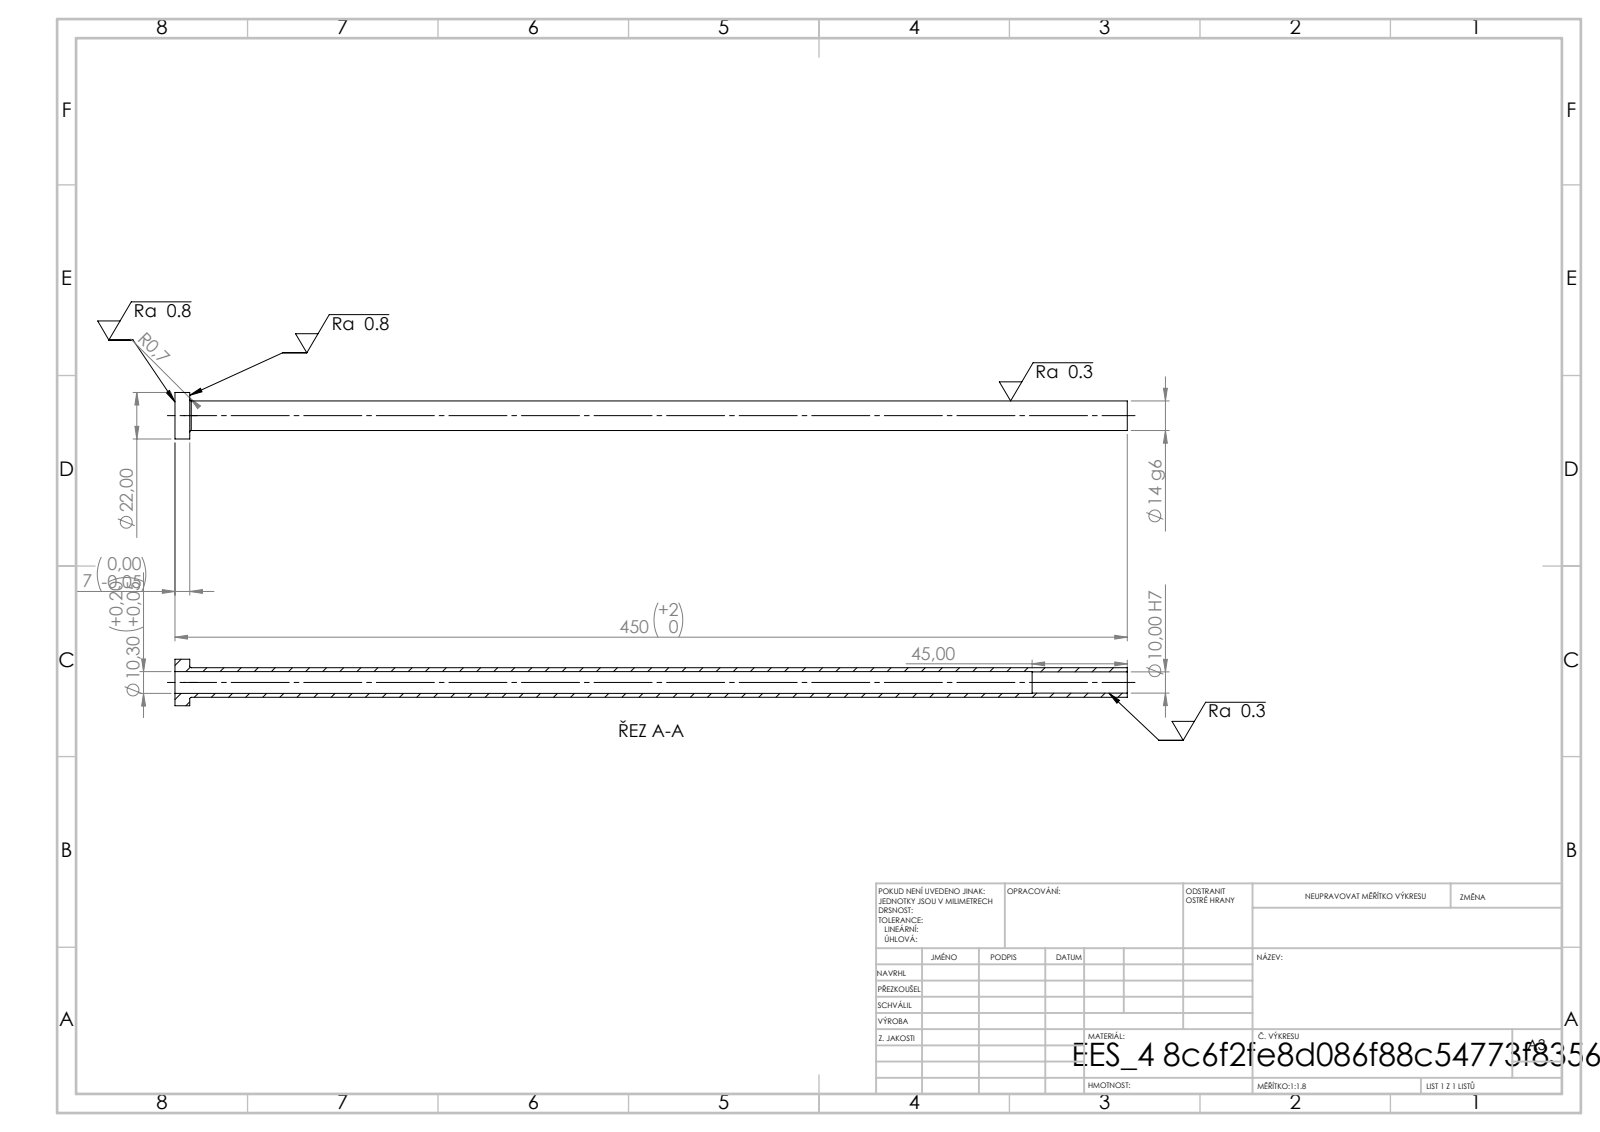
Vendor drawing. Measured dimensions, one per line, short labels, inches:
written by: SolidWorks 2019 (CONFIG_CONTROL_DESIGN)
unit: in
bodies: 1 solid, 14 faces (4 planar, 8 cylindrical, 2 other)
size: 17.717 × 0.866 × 0.866
volume: 2.049 in³; area: 54.37 in²
holes: 1× ⌀0.394, 1× ⌀0.406
bosses: 1× ⌀0.866, 1× ⌀0.551
face distances: 0.276, 17.717, 17.441, 15.945, 15.669, 1.772
